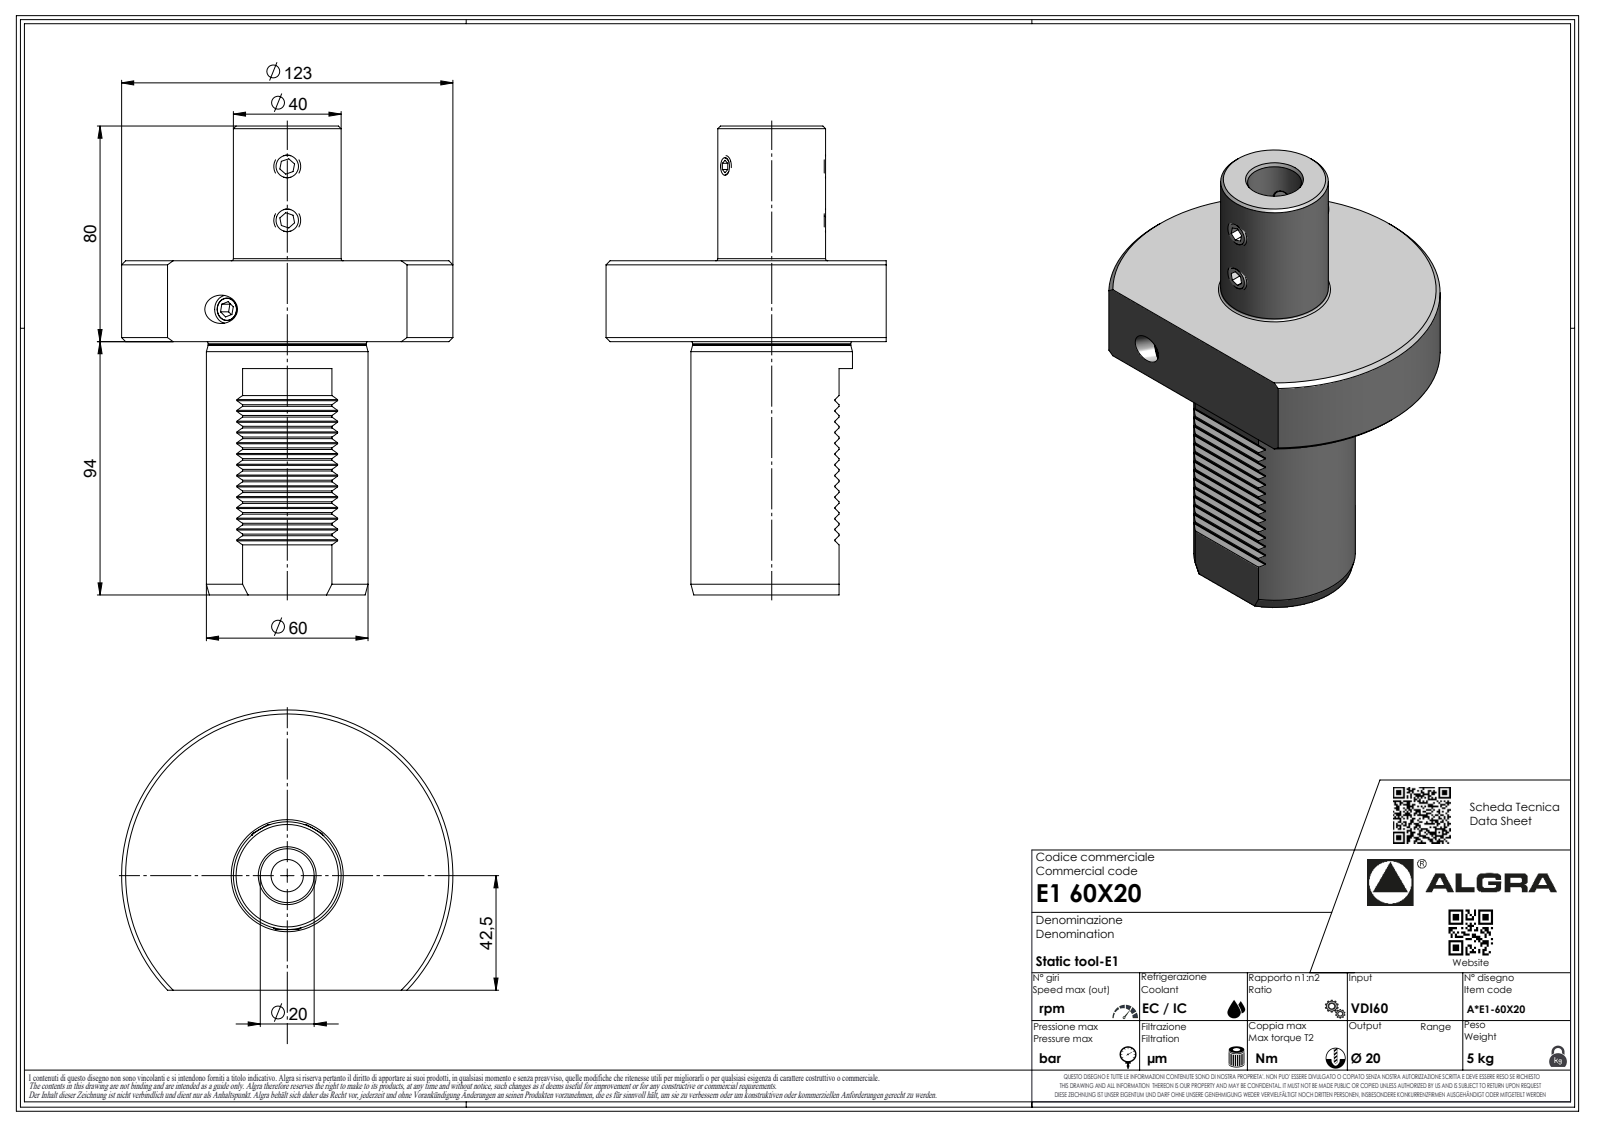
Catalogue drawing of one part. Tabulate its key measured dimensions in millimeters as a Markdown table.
| quantity | value |
| --- | --- |
| part name | E160X20 |
| STEP written by | SolidWorks 2023 (AUTOMOTIVE_DESIGN) |
| units | millimeters |
| bodies | 1 solid, 279 faces (187 planar, 45 cylindrical, 47 other) |
| overall size | 174 × 123 × 104 |
| volume | 620 801 mm³ |
| surface area | 59 986 mm² |
| round holes (diameter × count) | 2.1 × 1, 20 × 1 |
| round bosses / shafts (diameter × count) | 60 × 1, 58.7 × 1, 40 × 1, 6.37 × 1, 1.7 × 1 |
| partial cylindrical surfaces (radius × count) | 0.3 × 14, 0.33 × 7, 0.52 × 7, 3.7 × 7, 0.21 × 1, 61.5 × 1 |
| main face-to-face distances | 30, 94, 124, 2.83, 14.14, 11.31, 17.5, 8.48, 5.66, 16.97 |
